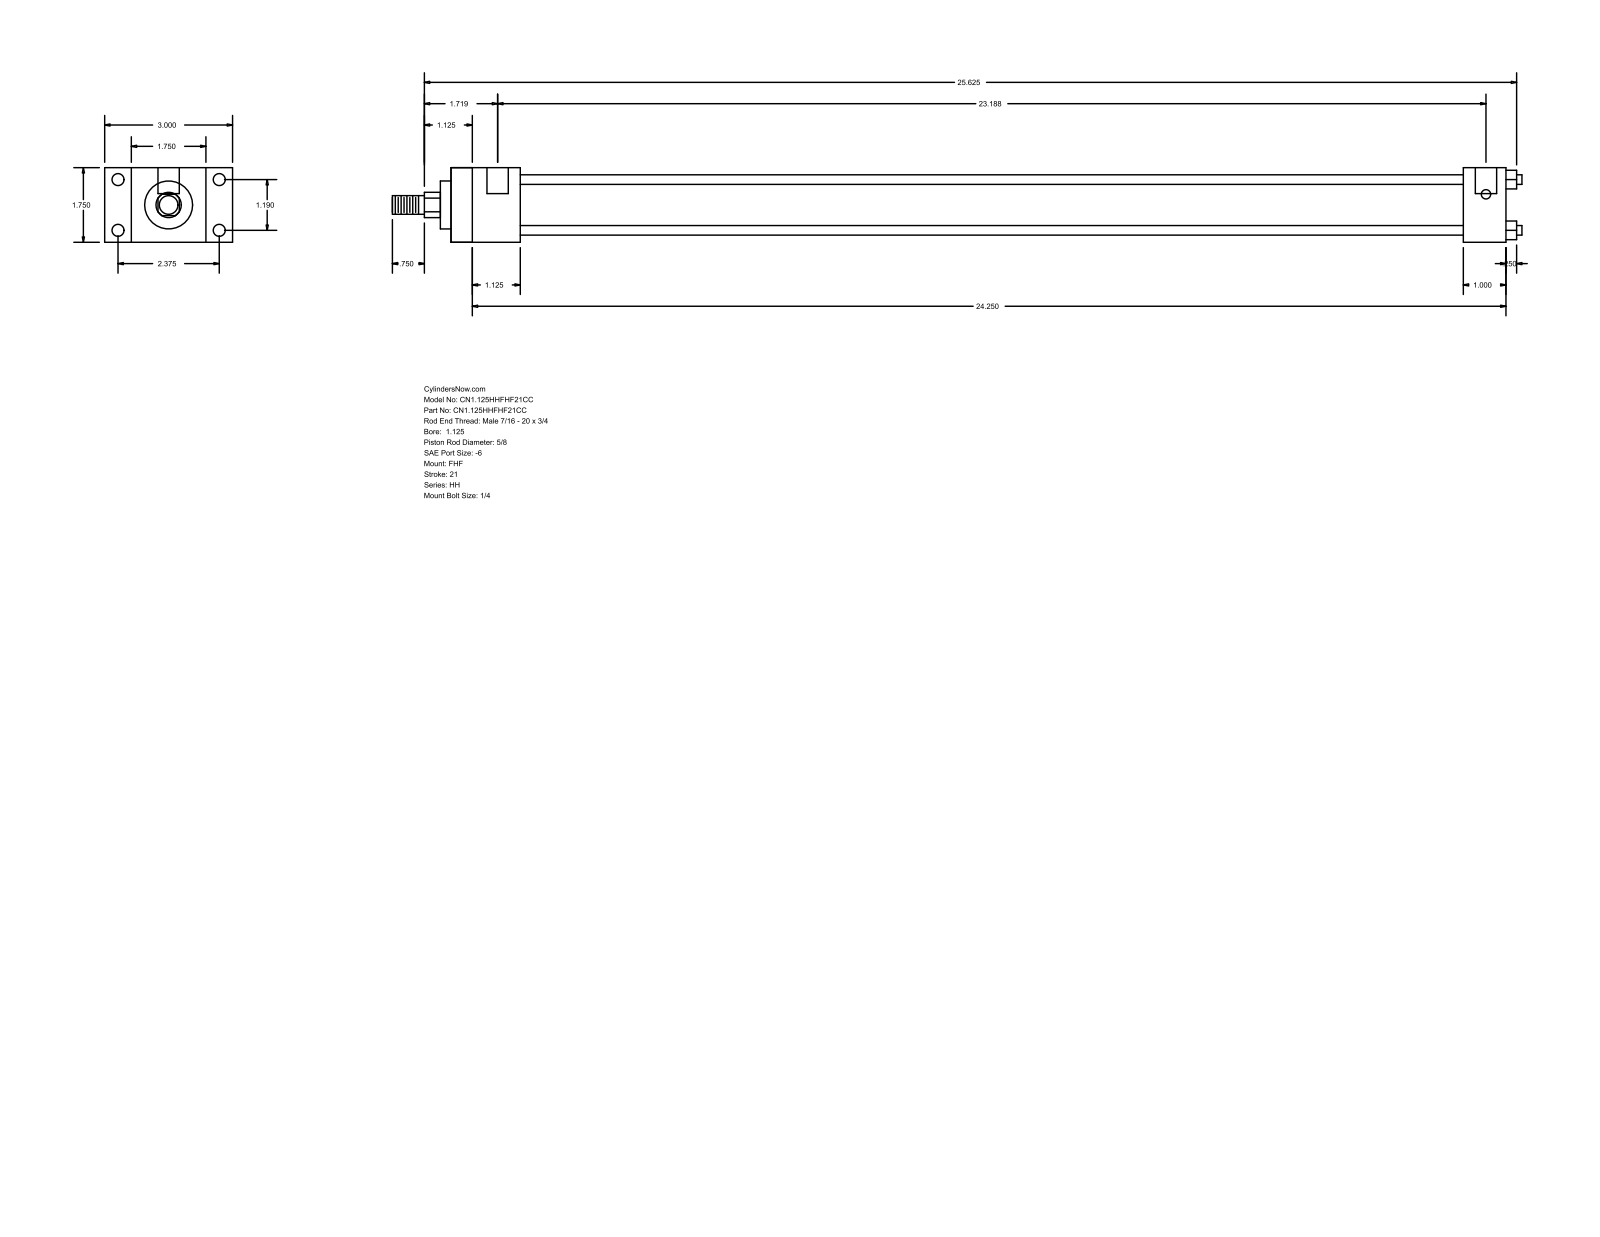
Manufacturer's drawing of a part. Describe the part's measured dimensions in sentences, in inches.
The part is named "HH_FHF__0112_0.625". Its 3-D file was written by "GSSL Pune (CONFIG_CONTROL_DESIGN)". It is 0 solids with 88 faces: 60 planar, 28 cylindrical and 0 other. Overall it measures 26.5 by 3 by 1.75 inches. Round holes: 4 of diameter 0.219, 4 of diameter 0.281, 2 of diameter 0.5. Round bosses or shafts: 4 of diameter 0.225, 1 of diameter 1.375, 1 of diameter 1.125, 1 of diameter 0.625, 1 of diameter 0.437. Partial cylindrical surfaces (rounded edges, fillets, slot ends): 1 of radius 0.297. The main face-to-face distances are 1.75, 0.625, 2.375, 1.625, 3, 24.75, 23.125, 1, 23.75, 22.125. The hole center spacings are 1.19, 2.375, 2.656, 23.063, 0.125, 23.187.
